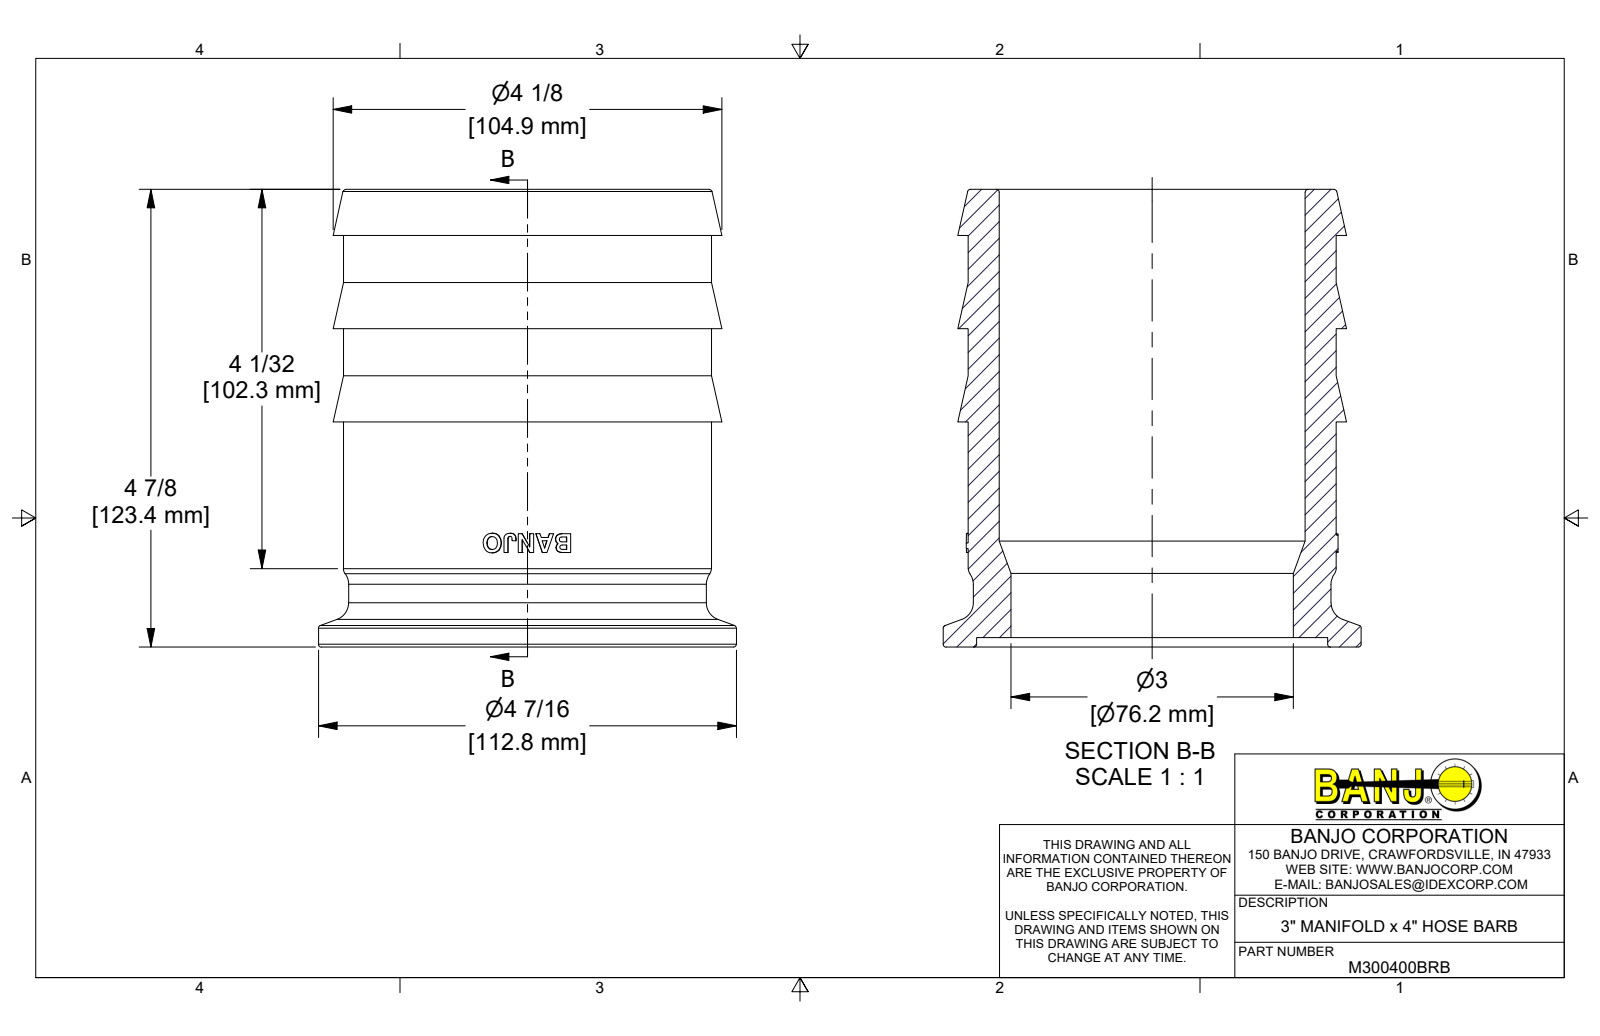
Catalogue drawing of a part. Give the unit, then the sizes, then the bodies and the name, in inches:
Units: inches
Overall size (bounding box): 4.86 × 4.44 × 4.44
Round holes (diameter × count): ⌀3 ×1, ⌀3.25 ×1, ⌀3.73 ×1
Round bosses / shafts (diameter × count): ⌀4.44 ×1, ⌀3.91 ×1, ⌀3.8 ×1
Partial cylindrical surfaces — rounded edges, fillets, slot ends (radius × count): R1.975 ×1
Main face-to-face distances: 0.1, 4.86, 4.76, 2.39, 3.38, 4.37, 2.29, 3.28, 4.27, 0.99
Volume: 20.52 in³ · Surface area: 128.9 in²
Bodies: 1 solid, 287 faces (87 planar, 37 cylindrical, 163 other)
Part name (STEP PRODUCT): M300400BRB
STEP written by: Autodesk Inventor 2022 (AUTOMOTIVE_DESIGN)
